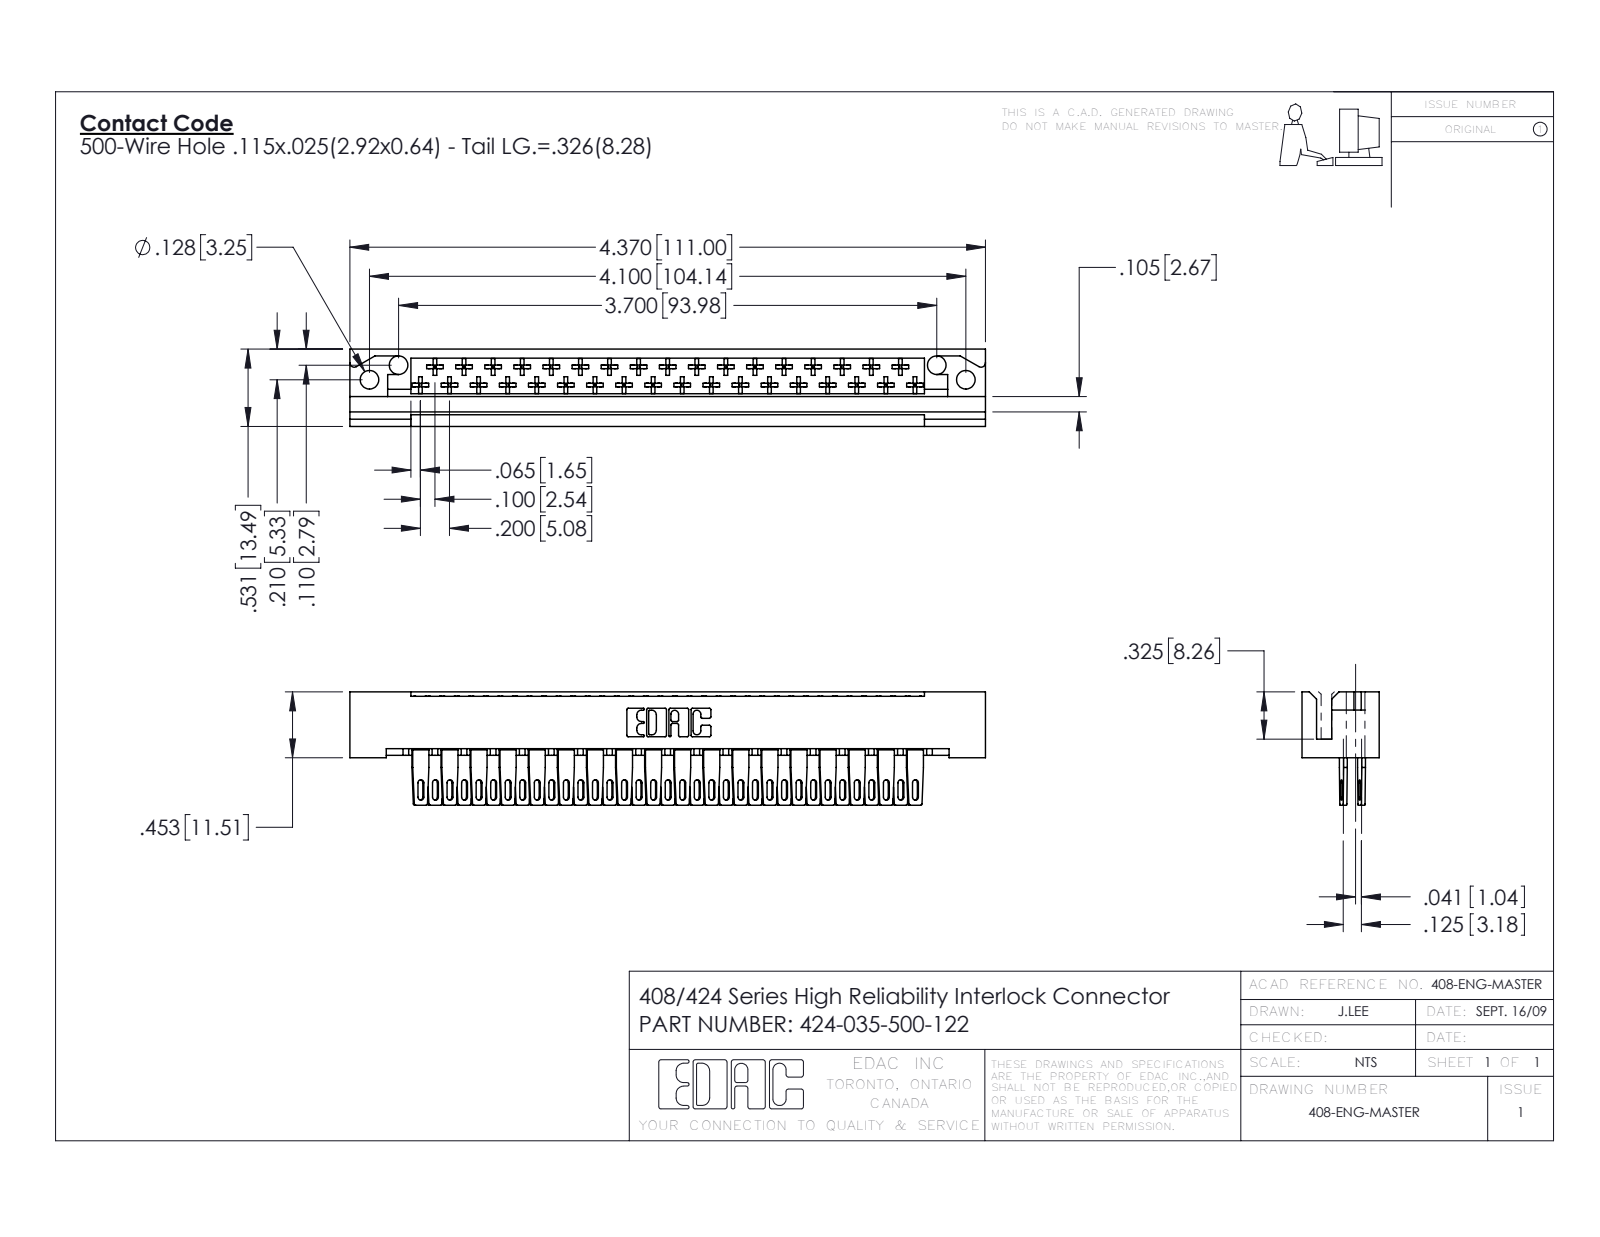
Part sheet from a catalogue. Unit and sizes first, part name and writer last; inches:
Units: inches
Overall size (bounding box): 4.37 × 0.779 × 0.531
Round holes (diameter × count): ⌀0.128 ×4
Partial cylindrical surfaces — rounded edges, fillets, slot ends (radius × count): R0.01 ×280, R0.021 ×70, R0.02 ×37, R0.01 ×22, R0.007 ×6, R0.031 ×6, R0.026 ×3, R0.03 ×2
Main face-to-face distances: 0.1, 0.296, 0.025, 0.531, 0.125, 0.326, 0.217, 0.235, 0.259, 0.272
Hole centre spacings: 0.224, 3.901, 3.7, 4.1
Volume: 0.72 in³ · Surface area: 25.3 in²
Bodies: 36 solids, 2140 faces (1524 planar, 476 cylindrical, 140 other)
Part name (STEP PRODUCT): 408-290-001_408-290-100; 424-035-500-122; 424 Part_035
STEP written by: SolidWorks 2016 (CONFIG_CONTROL_DESIGN)
